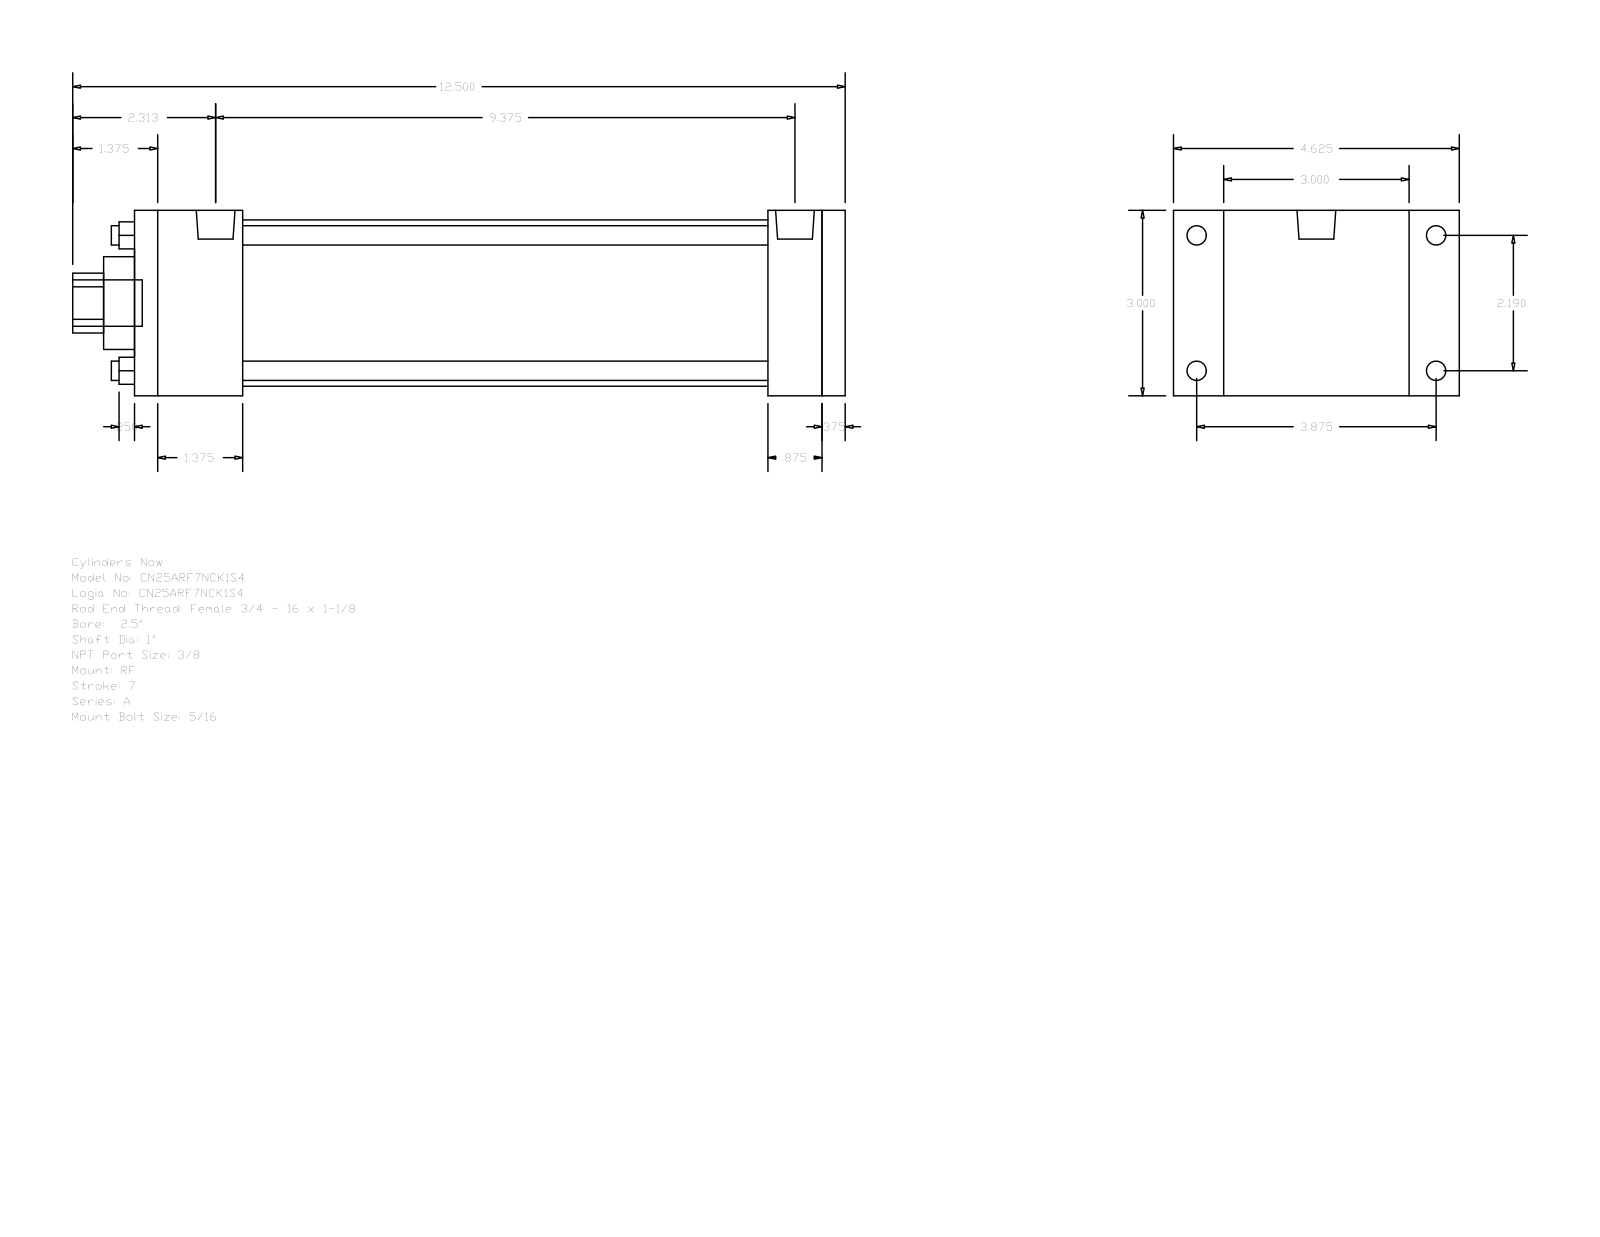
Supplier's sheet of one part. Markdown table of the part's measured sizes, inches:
| quantity | value |
| --- | --- |
| part name | A_RF__0250_1 |
| STEP written by | GSSL Pune (CONFIG_CONTROL_DESIGN) |
| units | inches |
| bodies | 0 solids, 92 faces (64 planar, 28 cylindrical, 0 other) |
| overall size | 12.5 × 4.625 × 3 |
| round holes (diameter × count) | 0.313 × 4, 1 × 1, 1.5 × 1, 2.69 × 1 |
| round bosses / shafts (diameter × count) | 0.313 × 4, 0.219 × 4, 0.627 × 2, 0.75 × 1 |
| partial cylindrical surfaces (radius × count) | 0.484 × 1 |
| main face-to-face distances | 3, 11.5, 0.375, 11.125, 1.75, 10.25, 8.5, 9.375, 9.75, 0.875 |
| hole center spacings | 1.548, 2.19, 3.097 |
